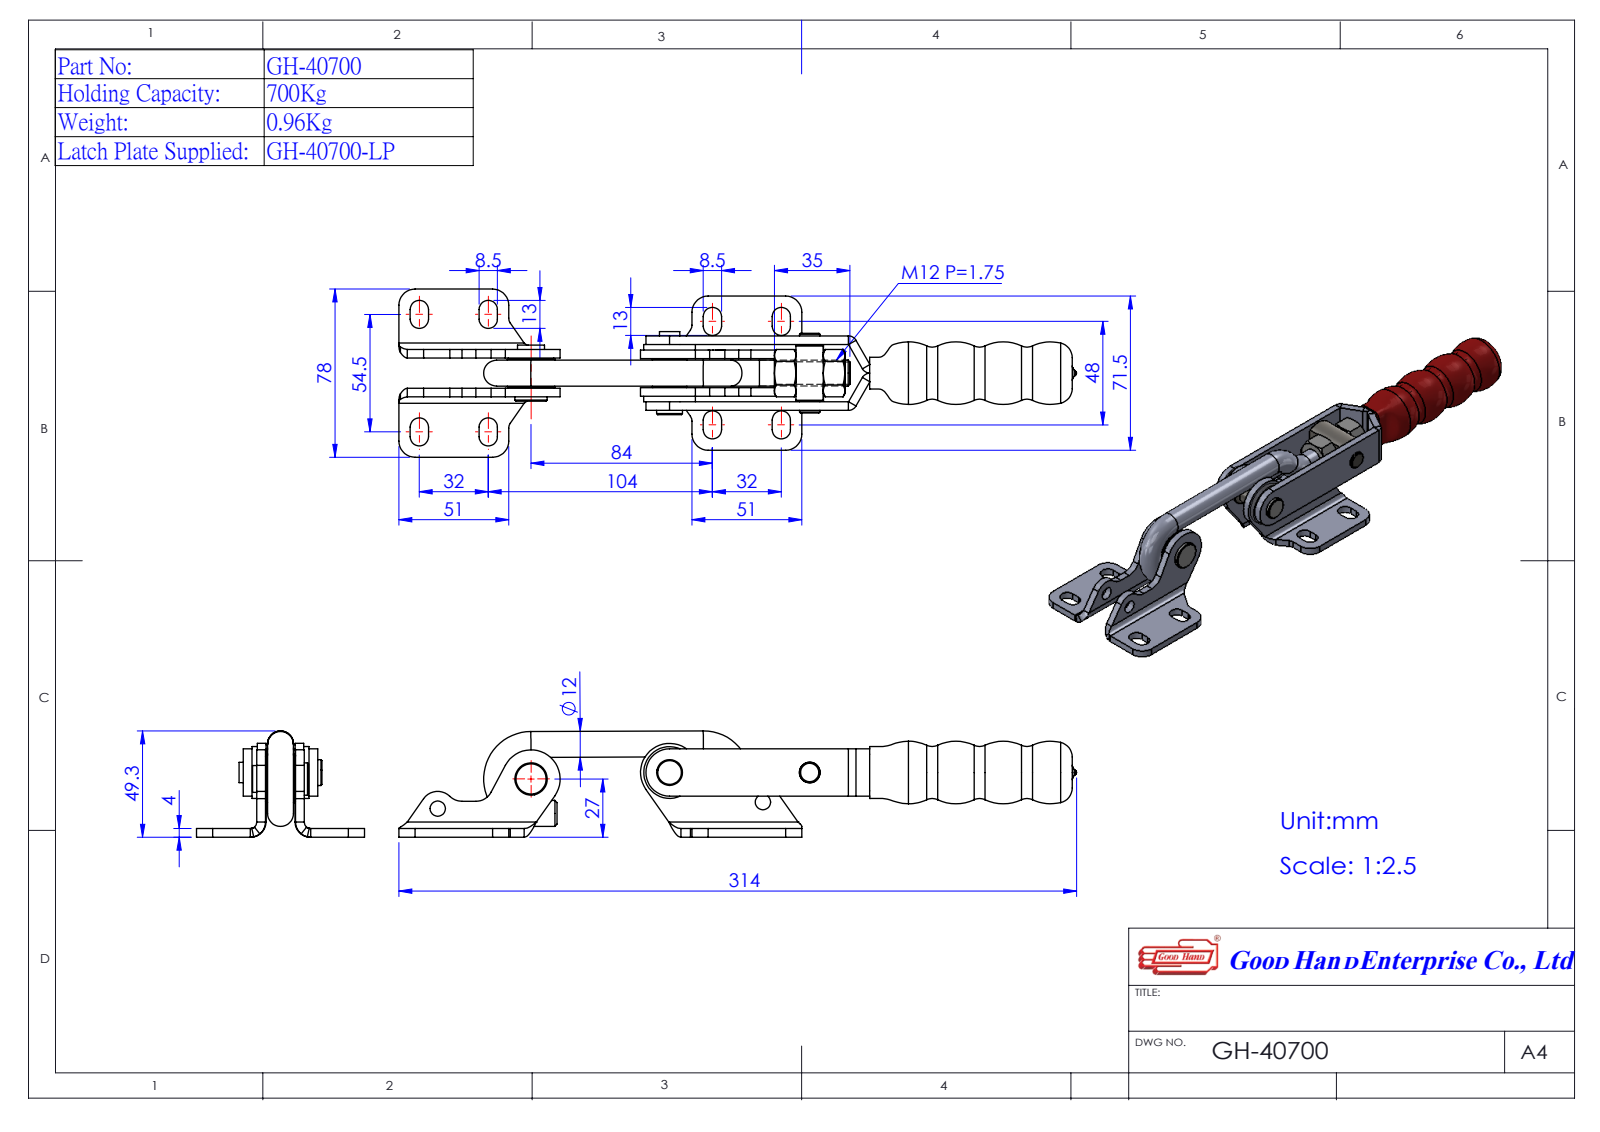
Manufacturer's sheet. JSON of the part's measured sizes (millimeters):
{"part_name": "440700SS44-1^GH-40700(簡化); Group1^GH-40700(簡化); Group3^GH-40700(簡化); GH-40700(簡化) (+2 more)", "step_written_by": "SolidWorks 2016 (AUTOMOTIVE_DESIGN)", "units": "millimeters", "bodies": {"solids": 6, "faces": 670, "planar": 280, "cylindrical": 157, "other": 233}, "overall_size": [314.49, 78, 49.31], "volume_mm3": 158506, "surface_area_mm2": 63484, "round_holes": [[3, 2], [7.1, 2], [8, 2], [1.53, 1], [10.2, 1], [12, 1]], "round_bosses_or_shafts": [[12, 3], [24, 1], [22, 1], [16, 1], [12.6, 1], [9.5, 1], [1.47, 1]], "partial_cylinders_radius": [[4.25, 16], [7.5, 8], [8, 6], [3, 4], [4, 4], [4.01, 4], [7, 4], [0.58, 3]], "face_to_face_distances": [4, 24, 6.5, 6.25, 24.25, 17.75, 30.5, 20, 28.25, 26.5], "hole_center_spacings": [19.77, 25.69, 27.97, 44, 45.43, 51.18, 60, 65]}
